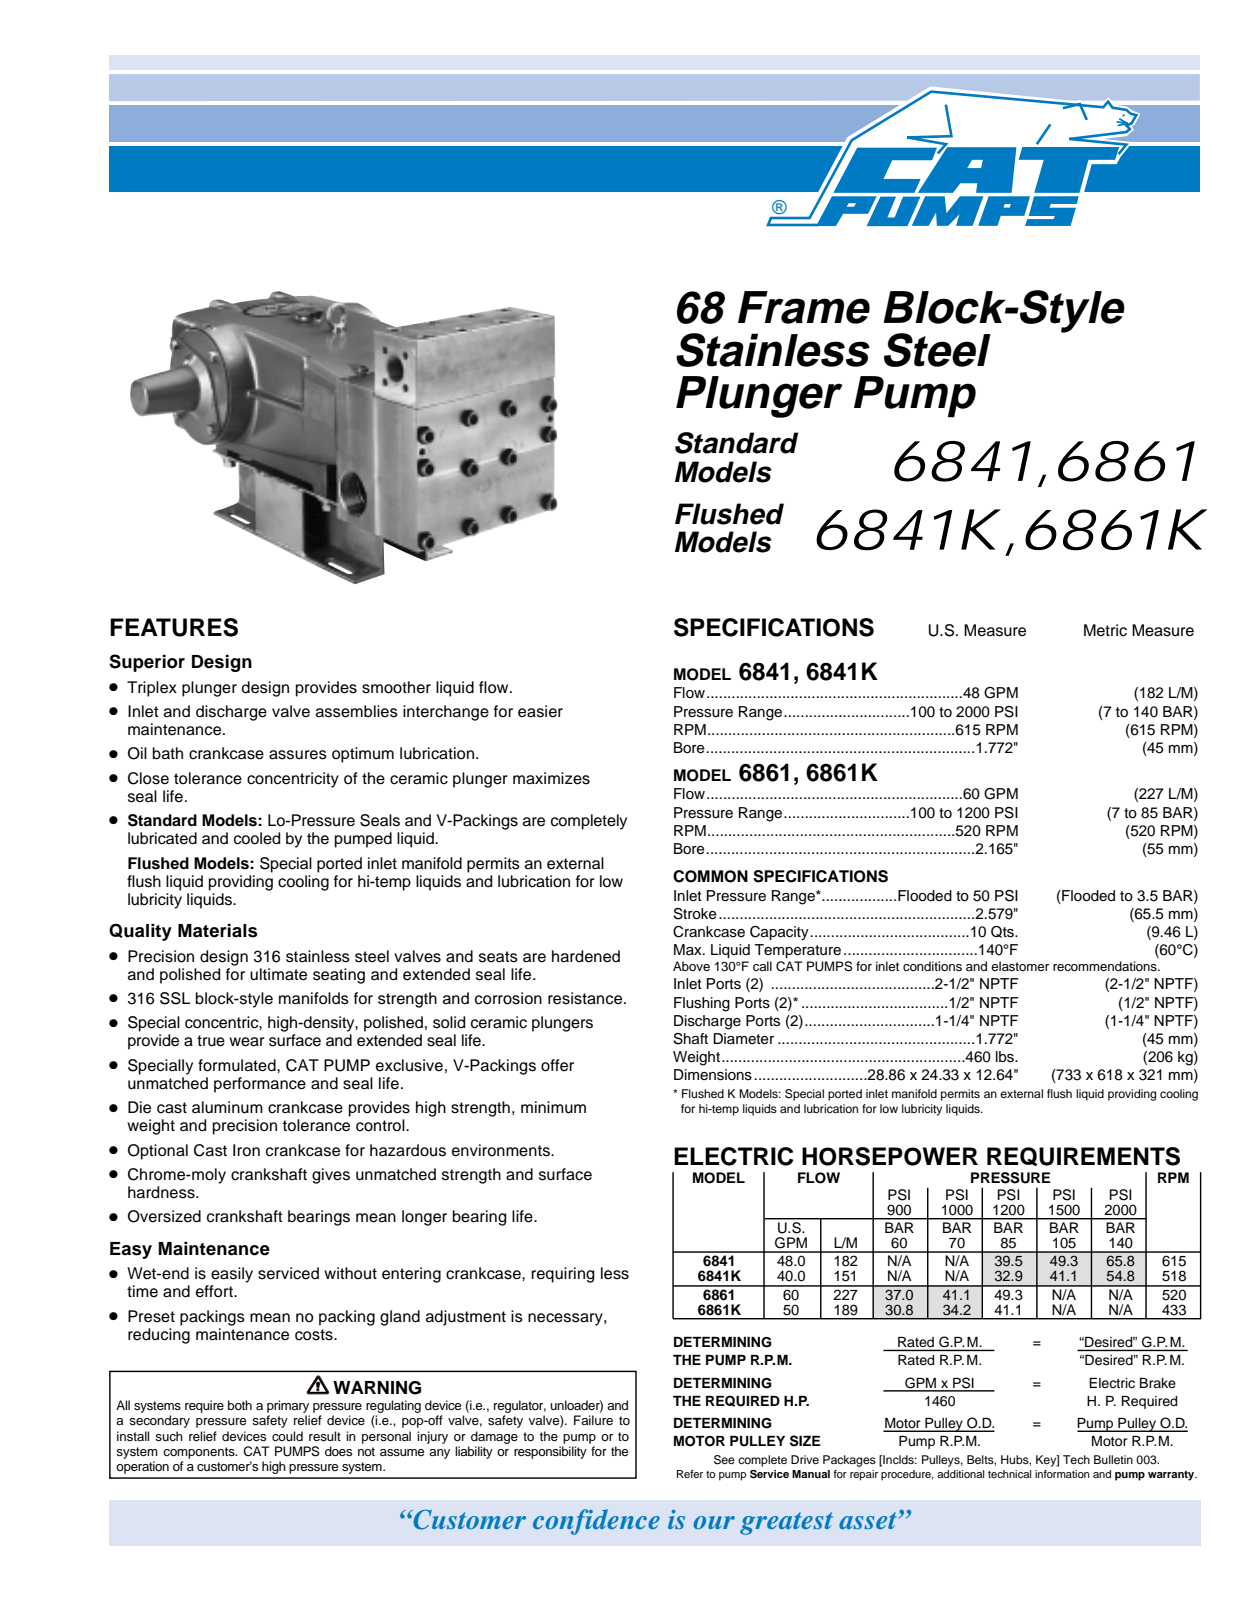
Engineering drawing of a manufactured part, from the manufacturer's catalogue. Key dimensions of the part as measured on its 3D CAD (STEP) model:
Part name (STEP PRODUCT): Socket Head Cap Screw_AM_B18.3.1M - 16 x 2.0 x 110 Hex SHCS 44NHX; Socket Head Cap Screw_AM_B18.3.1M - 16 x 2.0 x 110 Hex SHCS - 44NHX; 60fr_drive_end; 60FRAME_DRIVE_END (+8 more)
STEP written by: SolidWorks 2008 (AUTOMOTIVE_DESIGN)
Units: inches
Bodies: 82 solids, 2469 faces (1001 planar, 729 cylindrical, 739 other)
Overall size (bounding box): 28.975 × 24.016 × 13.15
Volume: 3 035 in³ · Surface area: 3 277 in²
Round holes (diameter × count): ⌀0.689 ×26, ⌀1.024 ×26, ⌀0.551 ×24, ⌀0.402 ×16, ⌀0.335 ×13, ⌀0.425 ×12, ⌀0.438 ×12, ⌀0.571 ×8, ⌀2.461 ×6, ⌀2.559 ×6, ⌀0.438 ×3, ⌀1.457 ×3
Round bosses / shafts (diameter × count): ⌀0.63 ×38, ⌀0.945 ×26, ⌀0.787 ×12, ⌀0.724 ×12, ⌀0.394 ×12, ⌀8.11 ×1, ⌀2.165 ×1, ⌀1.811 ×1
Partial cylindrical surfaces — rounded edges, fillets, slot ends (radius × count): R0.394 ×15, R0.197 ×13, R0.157 ×6, R0.294 ×4, R0.41 ×4, R0.51 ×4, R0.079 ×2, R0.276 ×2
Main face-to-face distances: 3.937, 4.094, 8.031, 0.039, 11.89, 1.494, 13.383, 2.204, 12.673, 0.711
Hole centre spacings: 3.346, 2.913, 1.004, 2.219, 2.408, 1.949, 5.483, 6.417
